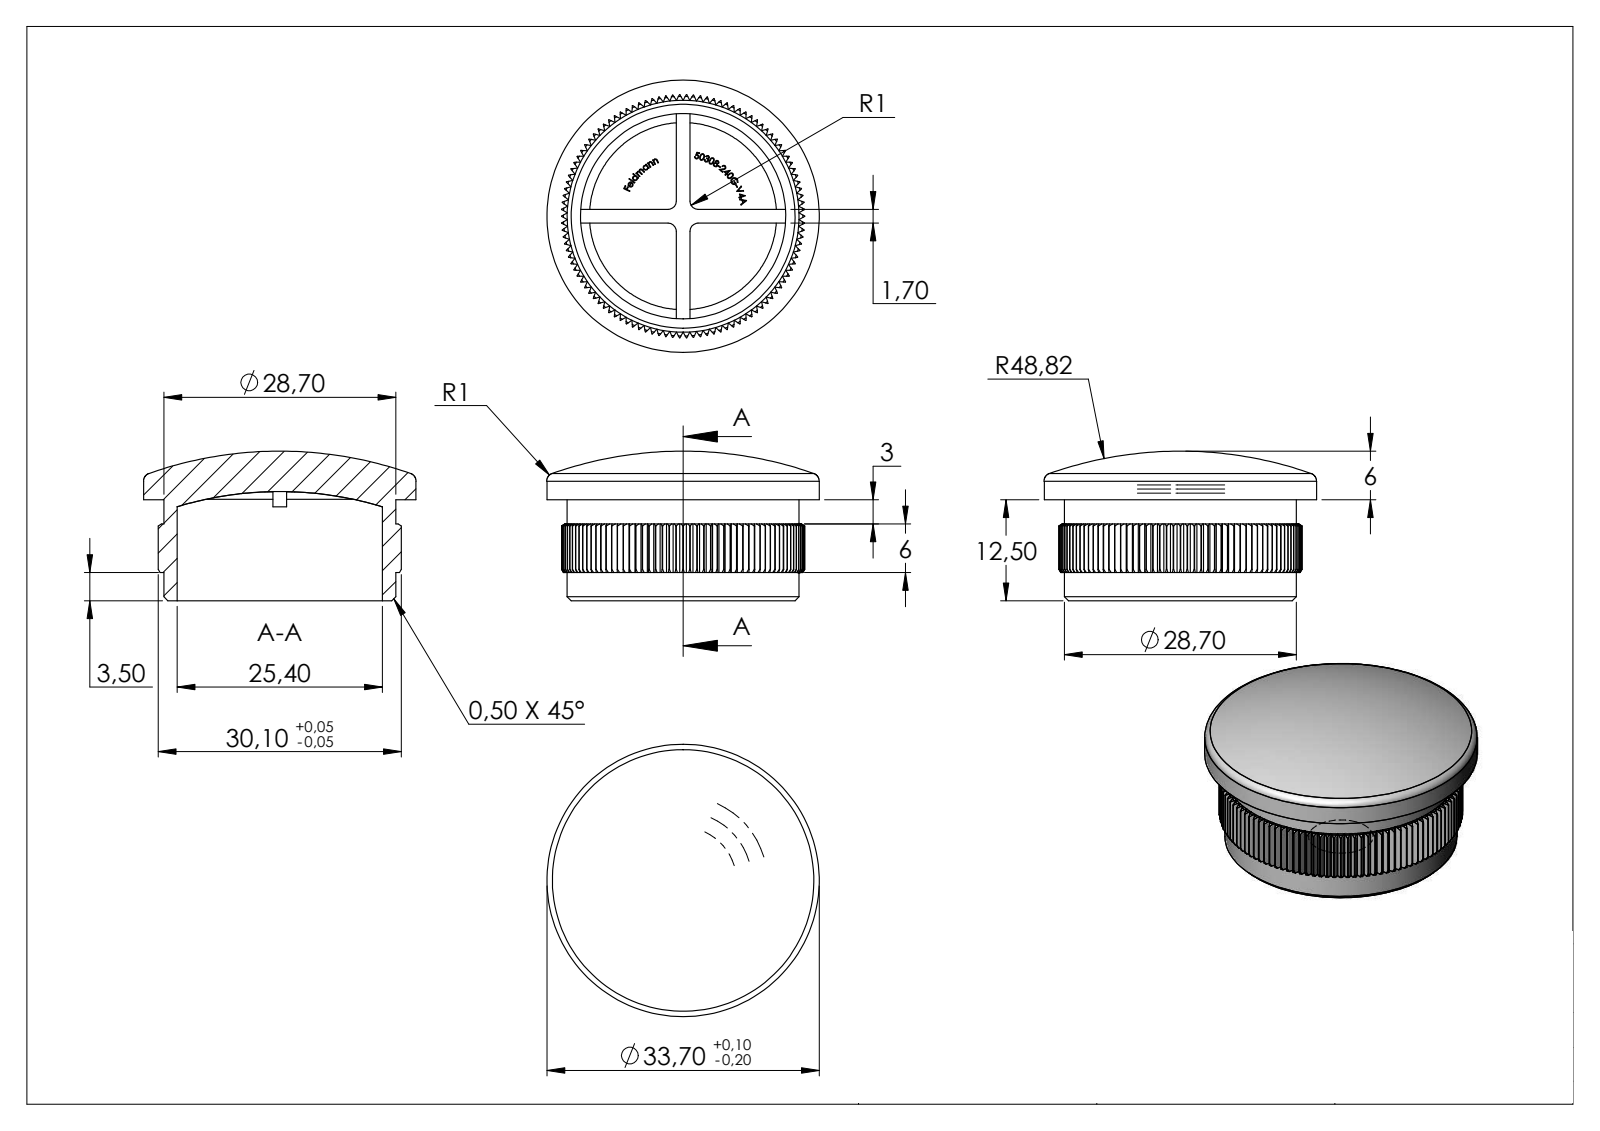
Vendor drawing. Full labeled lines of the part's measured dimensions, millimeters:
Part name (STEP PRODUCT): 50308-240G
STEP written by: SolidWorks 2015 (CONFIG_CONTROL_DESIGN)
Units: millimetres
Bodies: 1 solid, 1046 faces (540 planar, 118 cylindrical, 388 other)
Overall size (bounding box): 33.7 × 33.7 × 18.5
Volume: 5 081 mm³ · Surface area: 5 071 mm²
Round holes (diameter × count): ⌀25.4 ×1
Round bosses / shafts (diameter × count): ⌀33.7 ×1, ⌀28.7 ×1
Partial cylindrical surfaces — rounded edges, fillets, slot ends (radius × count): R1 ×4, R15.05 ×1
Main face-to-face distances: 14.36, 14.34, 12.5, 1.7, 3.5, 9, 9.5, 6, 3, 0.33
